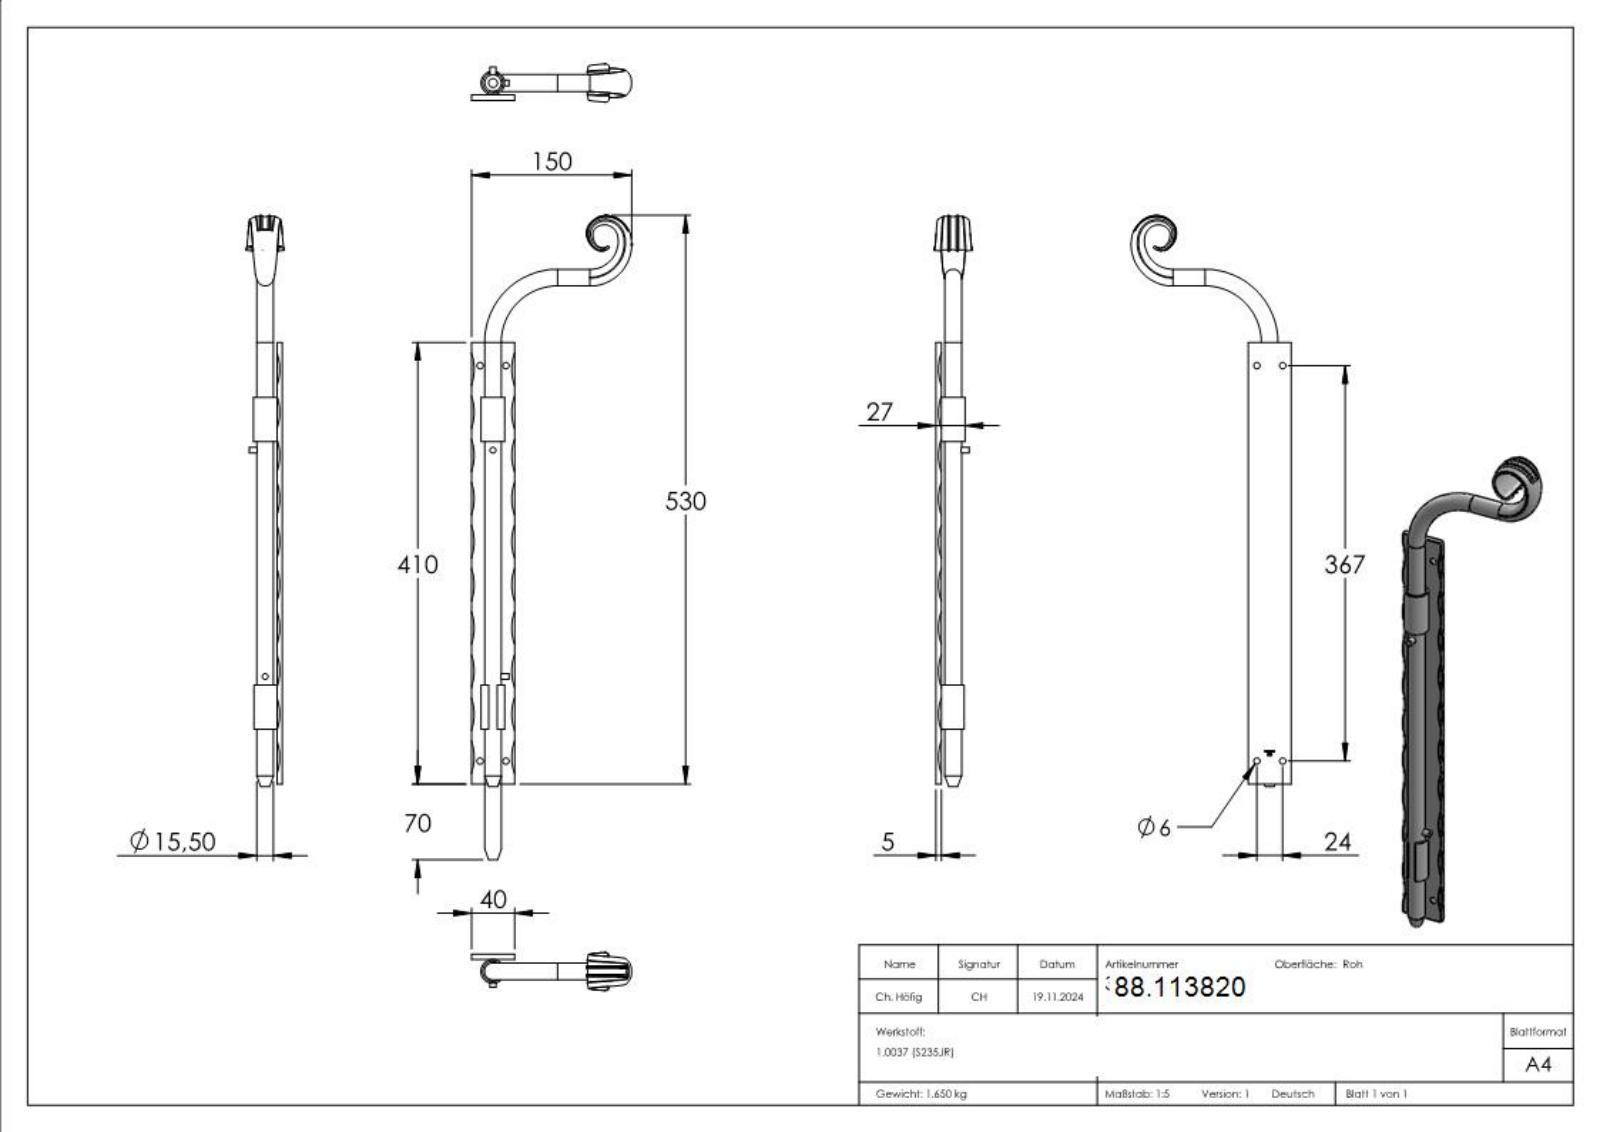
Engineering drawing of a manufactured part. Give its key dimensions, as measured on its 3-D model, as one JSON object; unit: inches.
{"part_name": "3820", "step_written_by": "SolidWorks 2018 (CONFIG_CONTROL_DESIGN)", "units": "inches", "bodies": {"solids": 4, "faces": 244, "planar": 98, "cylindrical": 12, "other": 134}, "overall_size": [20.869, 5.856, 1.417], "volume_in3": 12.9, "surface_area_in2": 126.7, "round_holes": [[0.236, 4], [0.74, 1]], "round_bosses_or_shafts": [[0.61, 2], [0.217, 2], [0.866, 1]], "face_to_face_distances": [0.197, 1.575, 16.142, 2.008, 3.622, 12.52, 14.134, 1.614, 10.512, 0.63], "hole_center_spacings": [0.945, 14.449, 14.48]}
